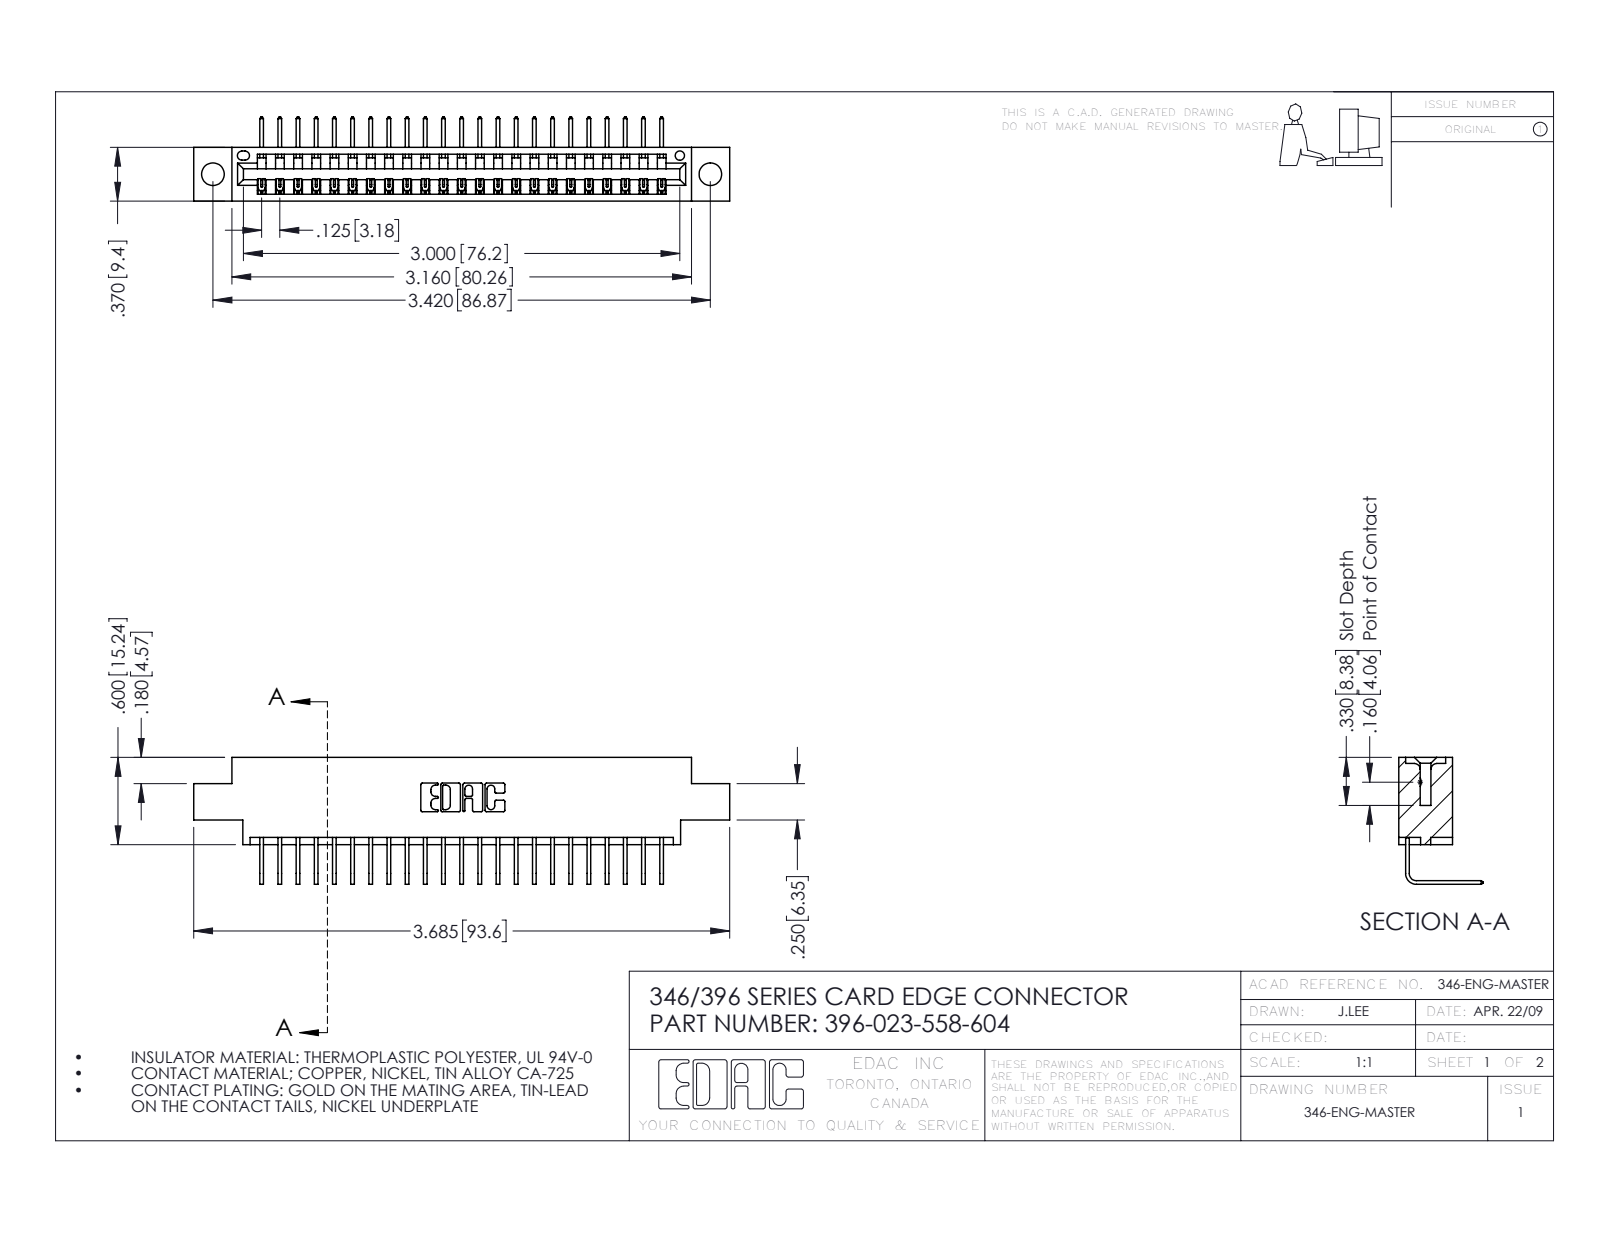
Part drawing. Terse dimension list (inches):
name: 346 Part_0.170 Offset - 0.156 Dia-TH; 345-292-001_558 Tail - 2; 396-023-558-604
written by: SolidWorks 2016 (CONFIG_CONTROL_DESIGN)
unit: in
bodies: 24 solids, 1506 faces (1046 planar, 460 cylindrical, 0 other)
size: 3.685 × 0.873 × 0.58
volume: 0.529 in³; area: 17.12 in²
holes: 2× ⌀0.156, 1× ⌀0.064
rounds: 46× R0.006, 22× R0.01, 6× R0.007, 6× R0.031, 3× R0.026, 2× R0.031, 2× R0.04, 1× R0.014
face distances: 0.322, 0.048, 0.37, 0.25, 0.298, 0.025, 0.072, 0.148, 0.222, 0.1
hole spacings: 0.246, 3.212, 3.42
